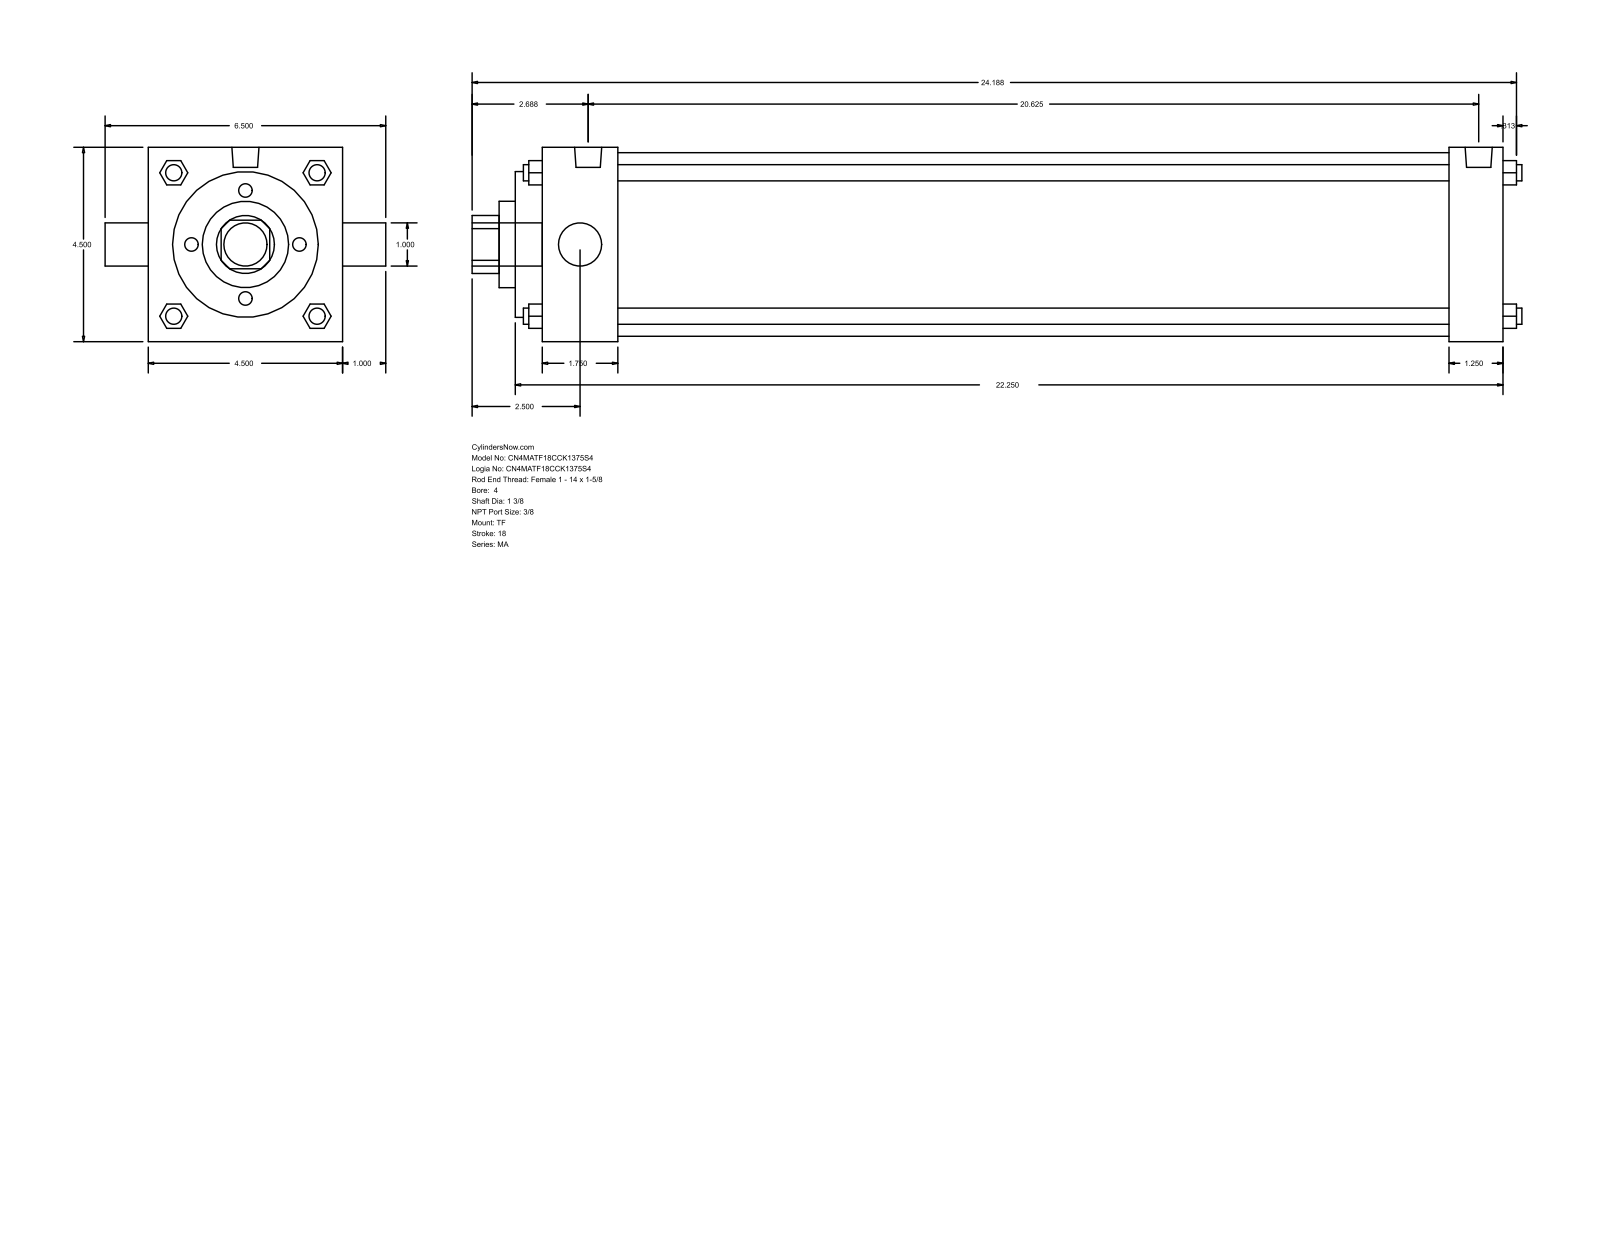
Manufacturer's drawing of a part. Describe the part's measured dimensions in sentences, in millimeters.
The part is named "MA_TF__0400_1.375". Its 3-D file was written by "GSSL Pune (CONFIG_CONTROL_DESIGN)". It is 0 solids with 122 faces: 93 planar, 29 cylindrical and 0 other. Overall it measures 617.54 by 165.1 by 114.3 millimeters. Round holes: 1 of diameter 25.4, 1 of diameter 34.92, 1 of diameter 50.8, 1 of diameter 85.72, 1 of diameter 107.95. Round bosses or shafts: 4 of diameter 9.53, 3 of diameter 11.11, 2 of diameter 15.93, 1 of diameter 25.4. Partial cylindrical surfaces (rounded edges, fillets, slot ends): 1 of radius 17.06. The main face-to-face distances are 114.3, 565.15, 581.02, 15.87, 549.27, 533.4, 31.75, 60.32, 44.45, 488.95.
